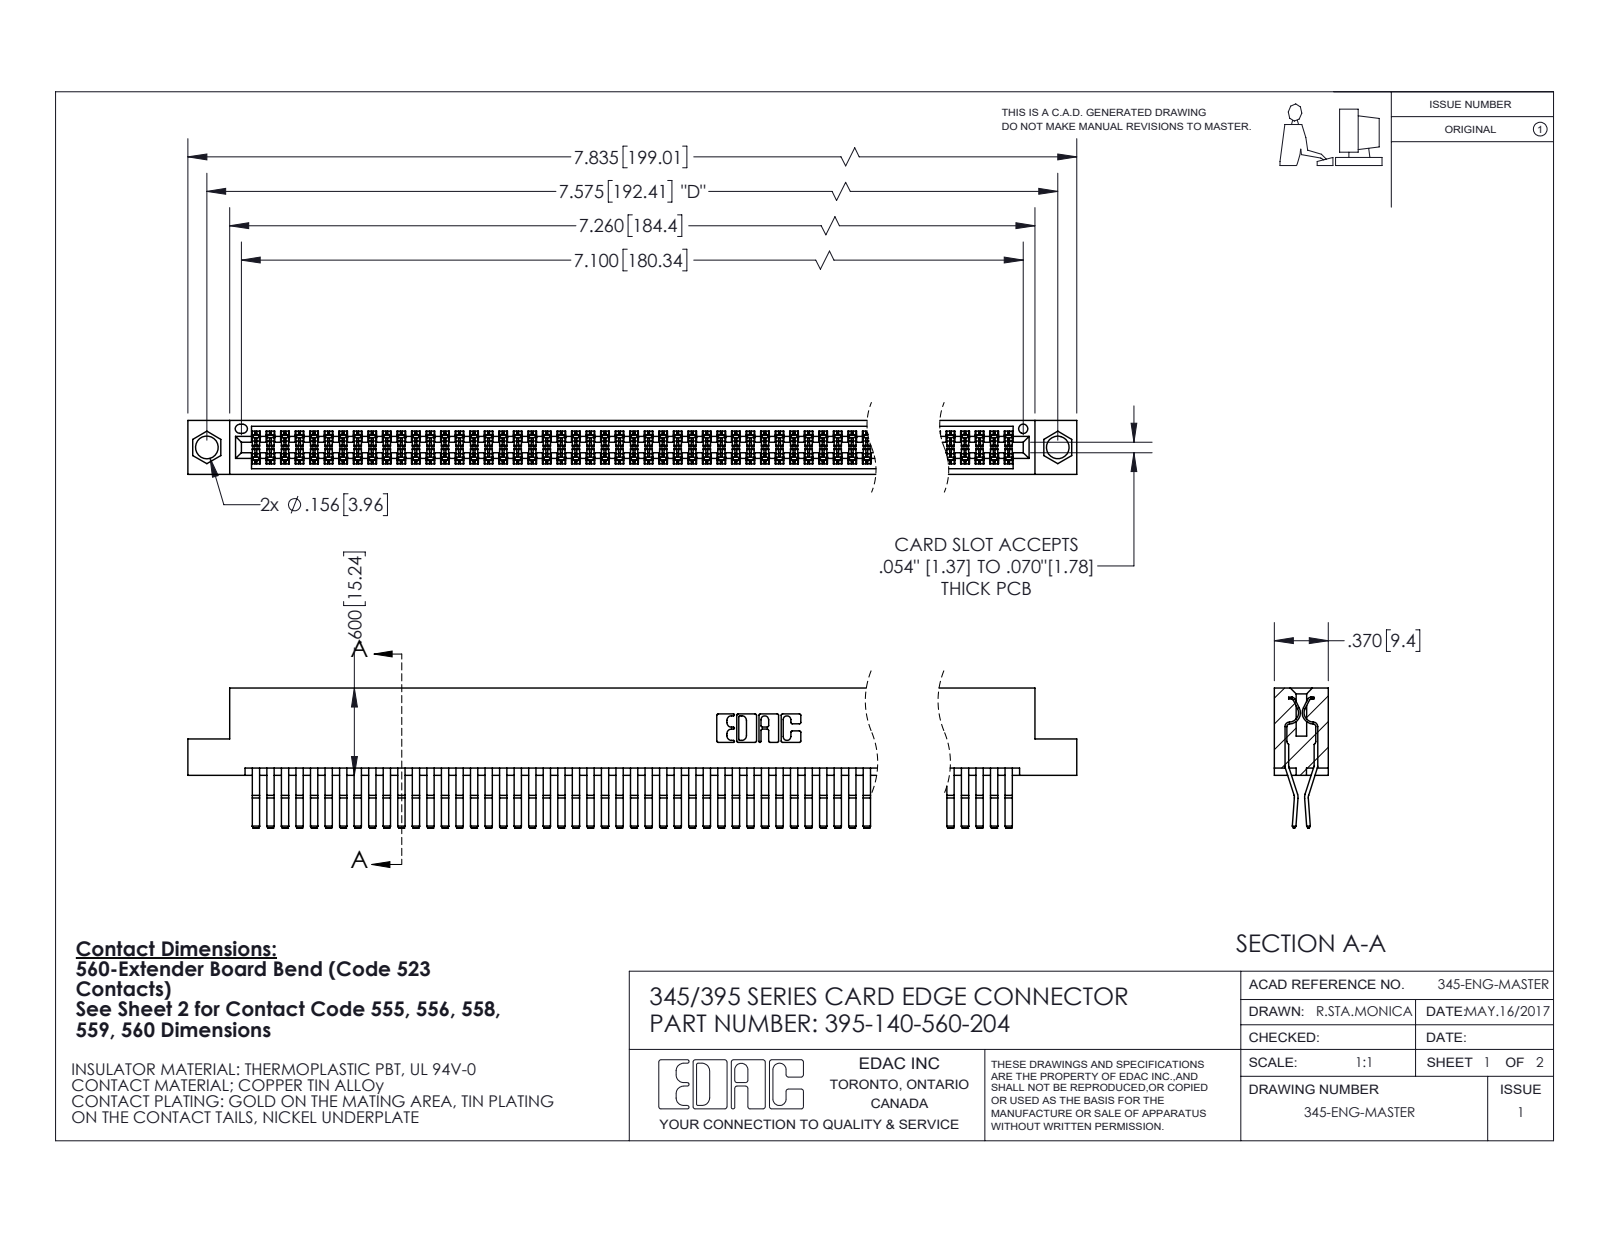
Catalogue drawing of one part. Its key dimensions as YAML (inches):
part_name: "345-292-001_560 Tail; 395-140-560-204; 345 Part_Flush Mounting Lugs - 0.156 Dia-TI"
step_written_by: "SolidWorks 2020 (CONFIG_CONTROL_DESIGN)"
units: inches
bodies: {solids: 141, faces: 7420, planar: 4714, cylindrical: 2706, other: 0}
overall_size: [7.835, 0.962, 0.37]
volume: 1.245
surface_area: 51.02
round_holes:
  - {diameter: 0.156, count: 2}
  - {diameter: 0.064, count: 1}
partial_cylinders:
  - {radius: 0.006, count: 210}
  - {radius: 0.01, count: 22}
  - {radius: 0.007, count: 6}
  - {radius: 0.031, count: 6}
  - {radius: 0.026, count: 3}
  - {radius: 0.01, count: 2}
  - {radius: 0.014, count: 2}
  - {radius: 0.019, count: 2}
face_to_face_distances: [0.025, 0.298, 0.072, 0.37, 0.2, 0.098, 0.272, 0.225, 0.175, 0.149]
hole_center_spacings: [0.27, 7.339, 7.575]
